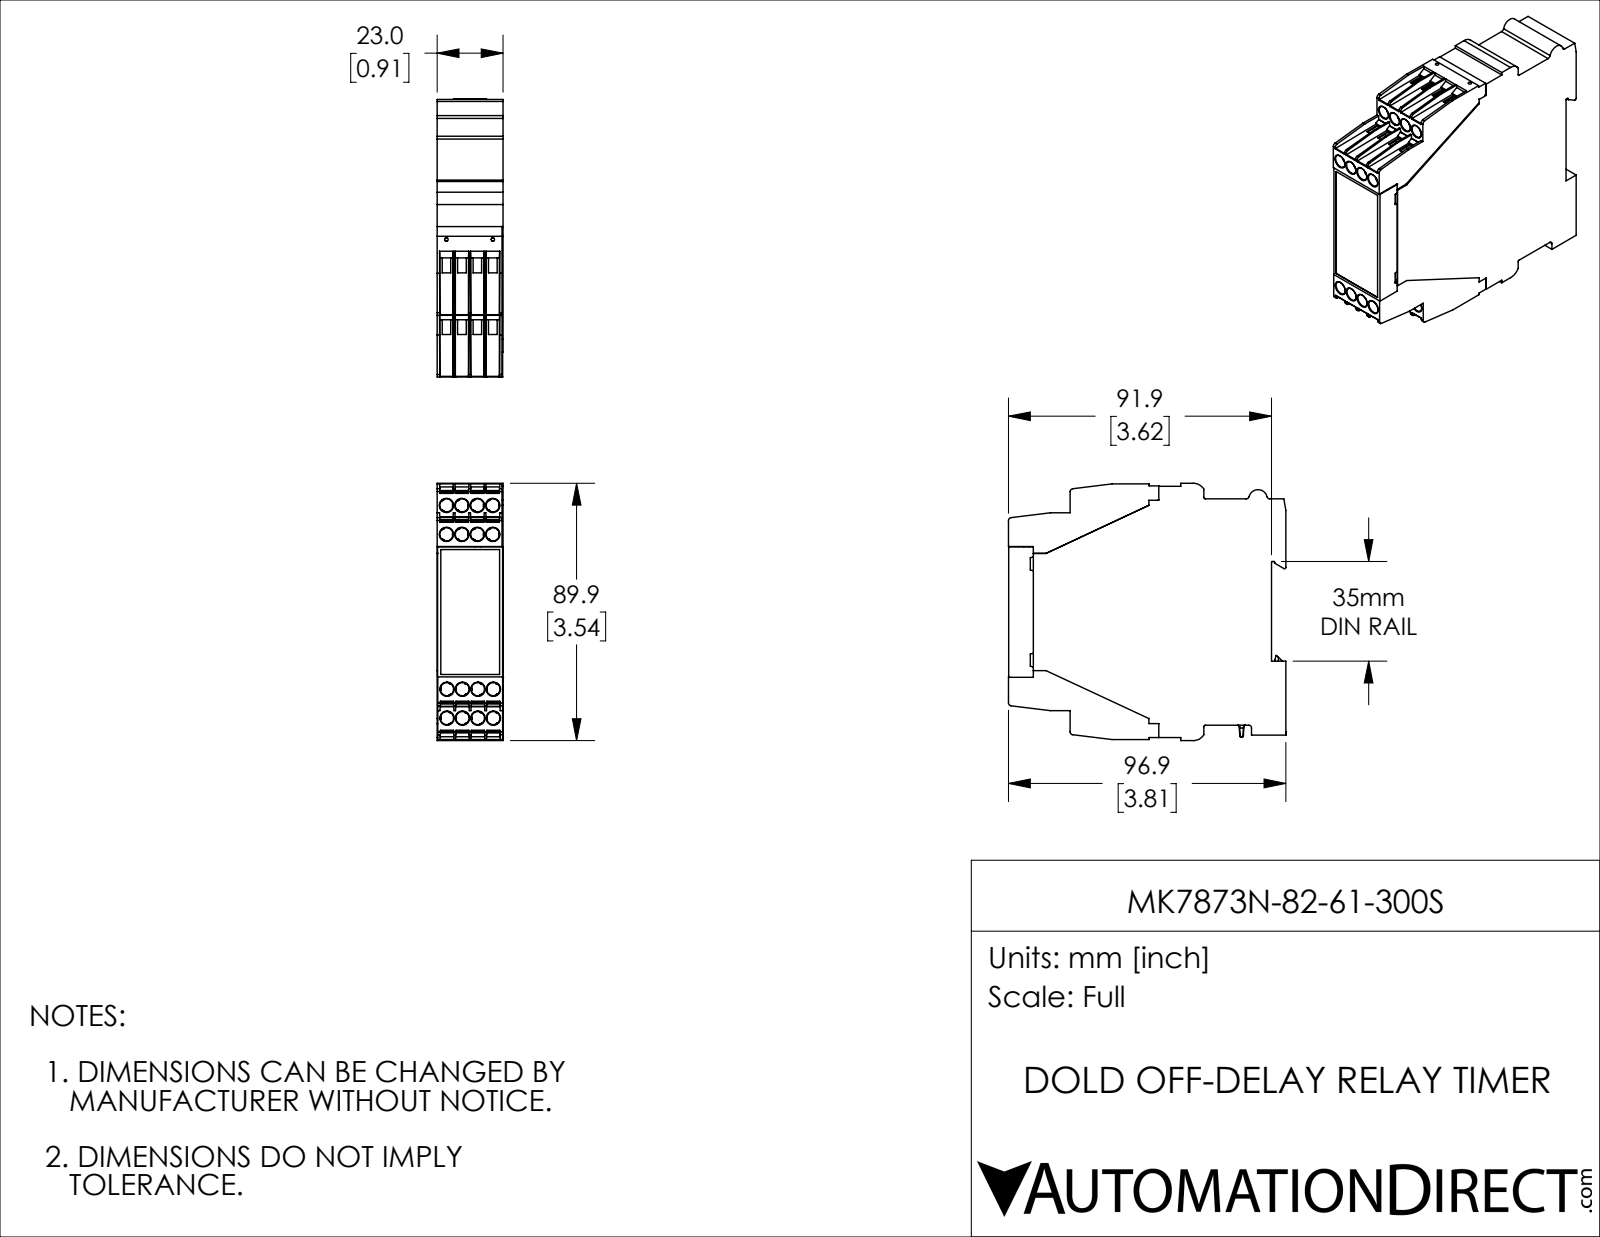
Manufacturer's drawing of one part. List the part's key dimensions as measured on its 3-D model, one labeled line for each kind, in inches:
Part name (STEP PRODUCT): MK7873N-82-61-300S
STEP written by: SolidWorks 2019 (CONFIG_CONTROL_DESIGN)
Units: inches
Bodies: 4 solids, 698 faces (556 planar, 99 cylindrical, 43 other)
Overall size (bounding box): 3.821 × 3.537 × 0.907
Volume: 10.55 in³ · Surface area: 53.84 in²
Round holes (diameter × count): ⌀0.181 ×16, ⌀0.047 ×4
Partial cylindrical surfaces — rounded edges, fillets, slot ends (radius × count): R0.039 ×11, R0.008 ×7, R0.02 ×7, R0.059 ×2, R0.174 ×2, R0.126 ×1
Main face-to-face distances: 0.906, 0.9, 0.894, 3.474, 3.809, 0.335, 3.278, 0.197, 3.612, 0.9
Hole centre spacings: 0.213, 0.451, 0.398, 0.425, 0.582, 2.526, 0.638, 2.534
